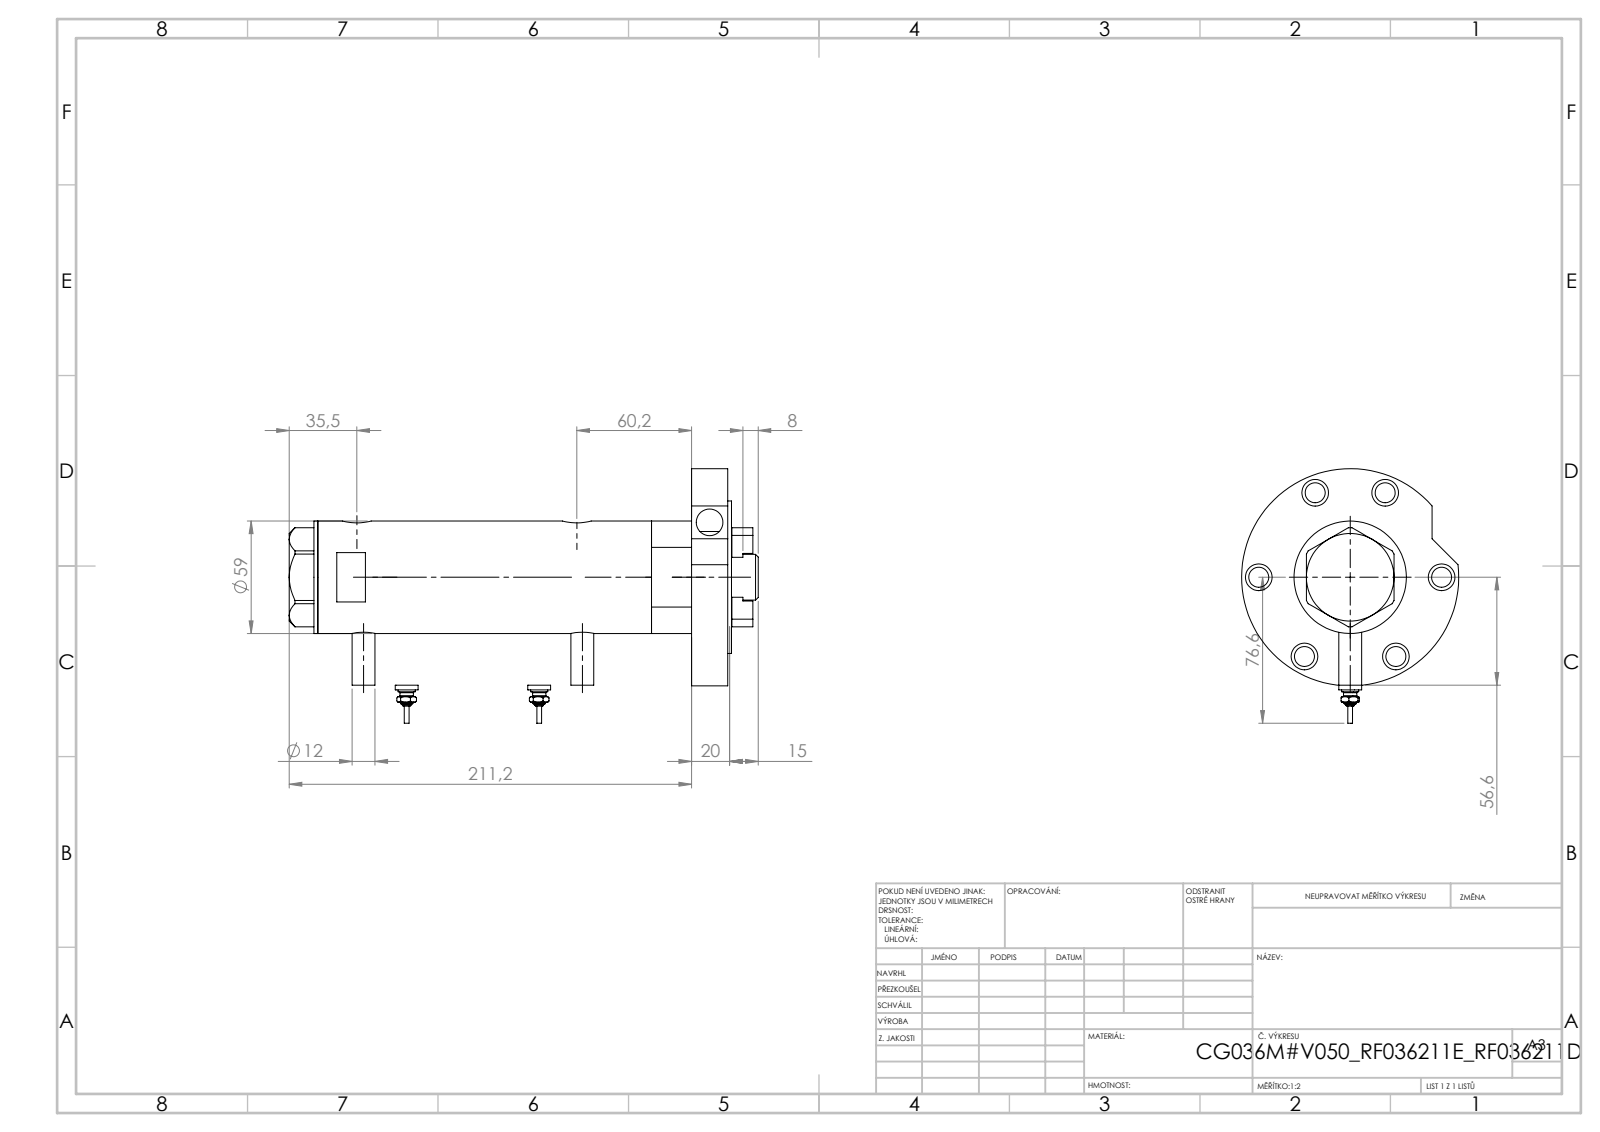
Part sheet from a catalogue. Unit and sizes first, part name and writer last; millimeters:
Units: millimetres
Overall size (bounding box): 246.2 × 133.6 × 114
Round holes (diameter × count): ⌀10.5 ×10, ⌀14 ×7, ⌀6.1 ×4, ⌀9.73 ×2, ⌀12.5 ×2, ⌀15 ×2, ⌀8.5 ×1, ⌀25 ×1, ⌀26.5 ×1, ⌀36 ×1, ⌀40 ×1, ⌀48 ×1
Round bosses / shafts (diameter × count): ⌀12 ×4, ⌀9 ×2, ⌀7 ×2, ⌀4.5 ×2, ⌀2.5 ×2, ⌀114 ×1, ⌀80 ×1, ⌀59 ×1
Main face-to-face distances: 2, 19, 21, 217.2, 196.2, 215.2, 137.2, 59, 78, 80
Hole centre spacings: 48, 19.92, 46.09, 57.24, 12, 28.22, 28.88, 35.17
Volume: 721 594 mm³ · Surface area: 154 811 mm²
Bodies: 9 solids, 296 faces (114 planar, 118 cylindrical, 64 other)
Part name (STEP PRODUCT): V270CG_MIDDLE; V270CG_RF211E; V270CG_BACK; V270CG_FRONT (+3 more)
STEP written by: SolidWorks 2019 (CONFIG_CONTROL_DESIGN)
